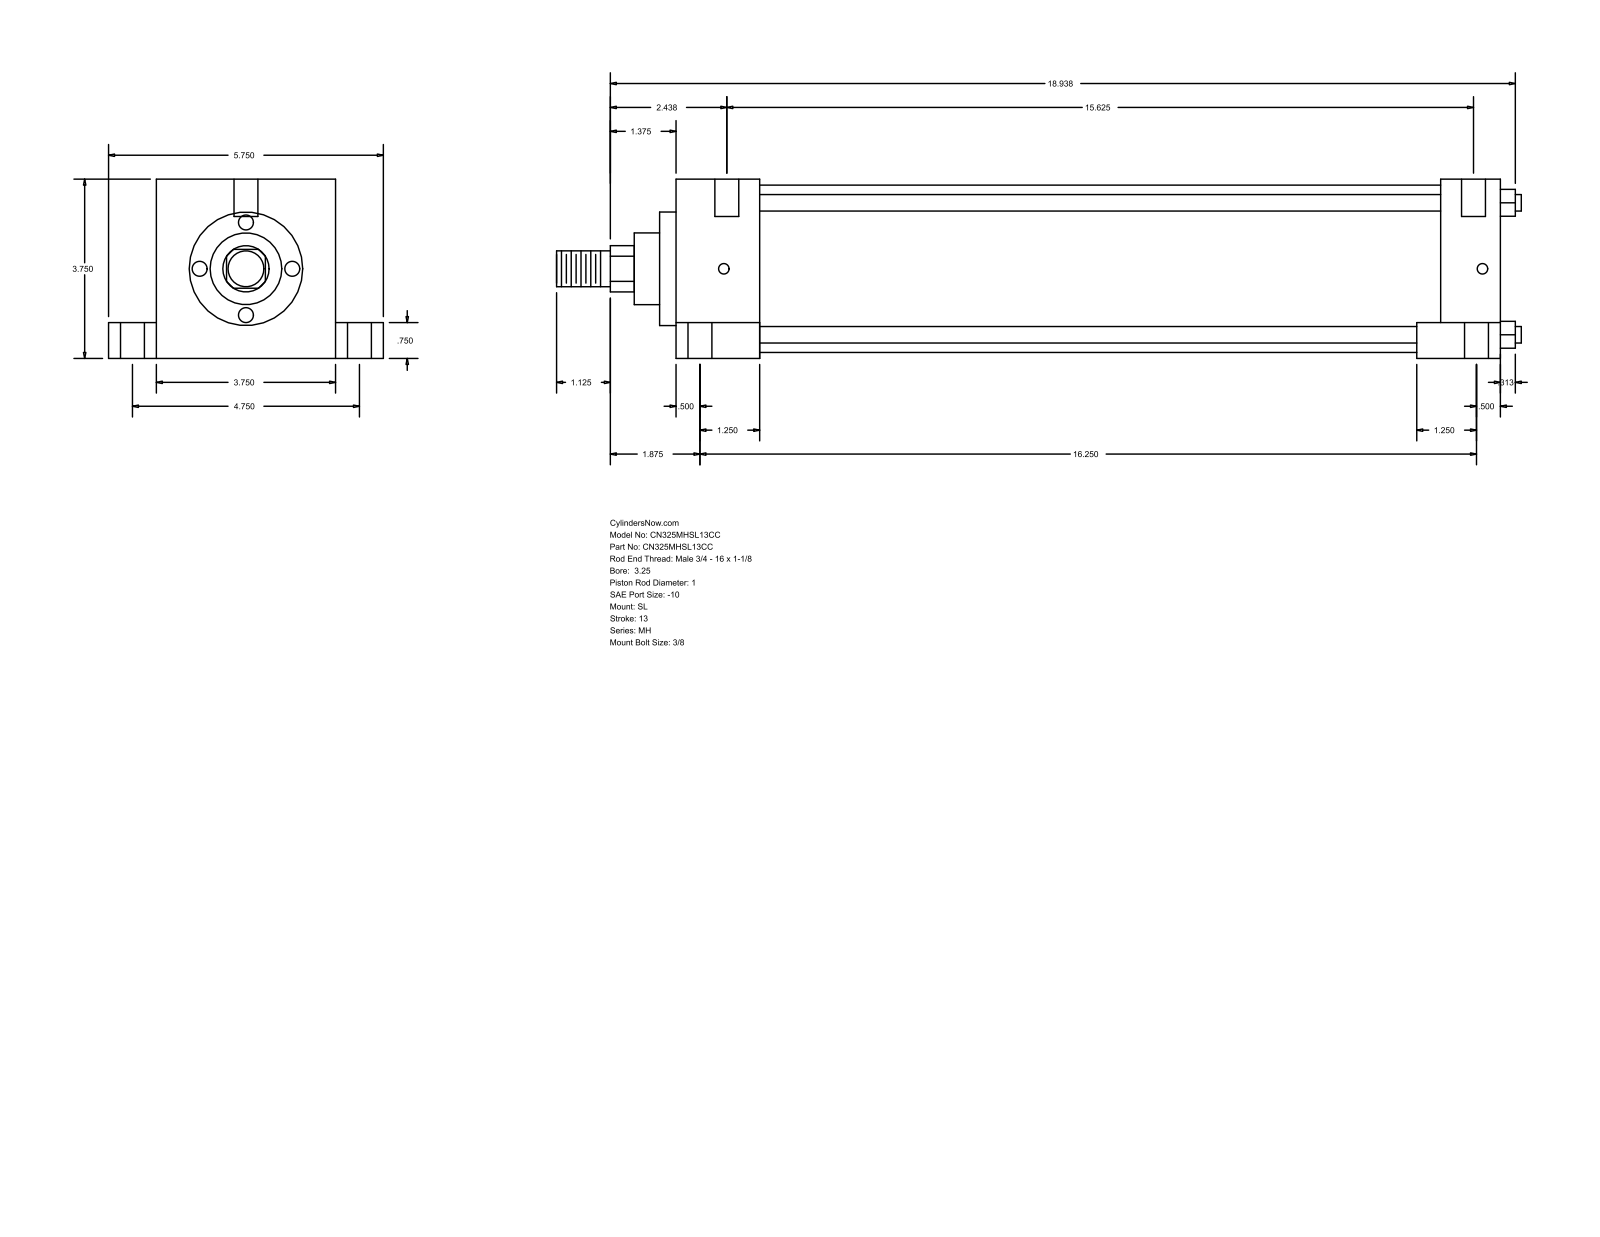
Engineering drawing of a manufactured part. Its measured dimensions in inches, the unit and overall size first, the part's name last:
Units: inches
Overall size (bounding box): 20.187 × 5.75 × 3.75
Round holes (diameter × count): ⌀0.5 ×6, ⌀0.219 ×4, ⌀0.75 ×4
Round bosses / shafts (diameter × count): ⌀0.345 ×4, ⌀3.5 ×1, ⌀2.375 ×1, ⌀1.5 ×1, ⌀1 ×1, ⌀0.75 ×1
Partial cylindrical surfaces — rounded edges, fillets, slot ends (radius × count): R0.484 ×1
Main face-to-face distances: 3.75, 17.25, 1.75, 15.5, 1, 4.75, 0.75, 3, 16, 14.25
Hole centre spacings: 2.376, 2.378, 2.427, 2.441, 4.75, 15.867, 15.875, 15.928
Bodies: 0 solids, 110 faces (77 planar, 33 cylindrical, 0 other)
Part name (STEP PRODUCT): MH_SL__0325_1
STEP written by: GSSL Pune (CONFIG_CONTROL_DESIGN)
